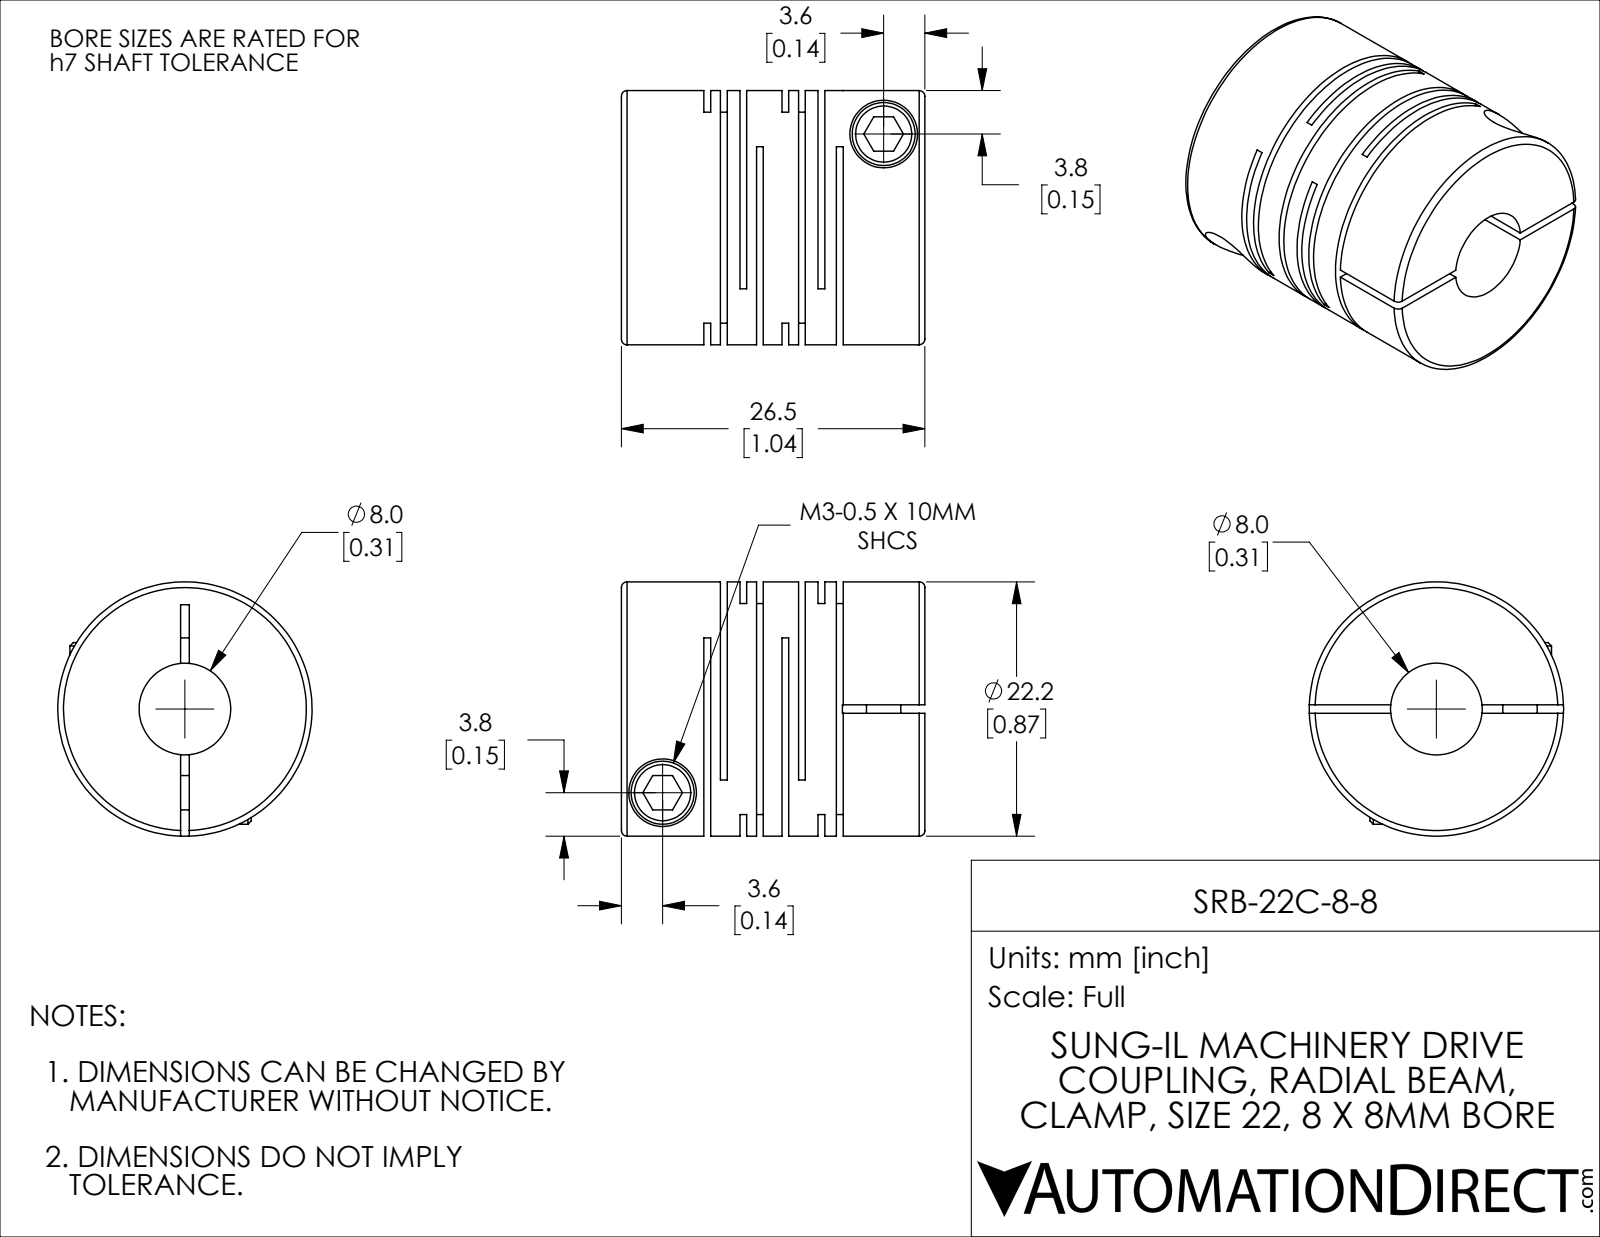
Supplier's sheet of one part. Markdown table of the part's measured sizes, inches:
| quantity | value |
| --- | --- |
| part name | SRB-22C-8-8 |
| STEP written by | SolidWorks 2021 (CONFIG_CONTROL_DESIGN) |
| units | inches |
| bodies | 1 solid, 115 faces (60 planar, 42 cylindrical, 13 other) |
| overall size | 1.043 × 0.874 × 0.874 |
| volume | 0.446 in³ |
| surface area | 12.18 in² |
| round holes (diameter × count) | 0.118 × 2, 0.232 × 2, 0.315 × 1 |
| round bosses / shafts (diameter × count) | 0.217 × 2, 0.874 × 1 |
| main face-to-face distances | 0.023, 0.124, 0.269, 0.057, 0.211, 0.067, 0.144, 0.245, 0.034, 0.101 |
